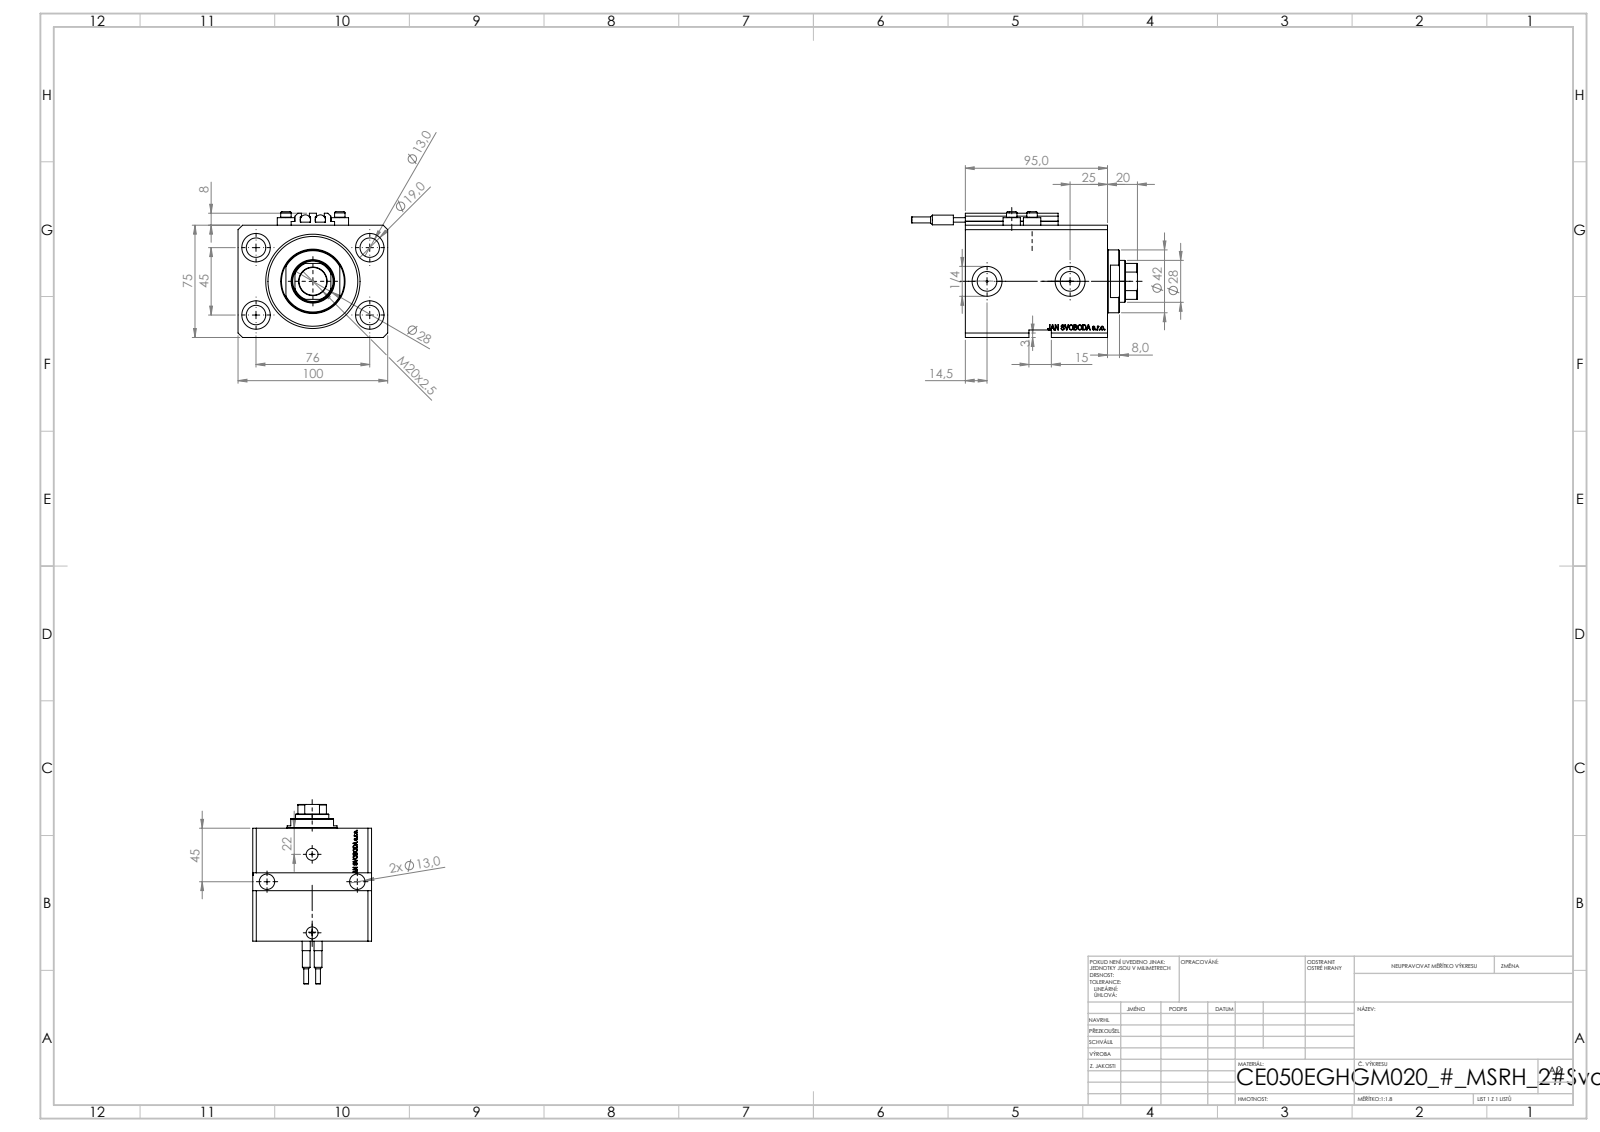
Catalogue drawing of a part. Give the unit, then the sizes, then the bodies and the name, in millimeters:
Units: millimetres
Overall size (bounding box): 151 × 100 × 84
Round holes (diameter × count): ⌀13 ×6, ⌀1.25 ×4, ⌀4 ×4, ⌀19 ×4, ⌀10 ×2, ⌀13.16 ×2, ⌀20 ×2, ⌀18.5 ×1, ⌀28 ×1, ⌀50 ×1, ⌀63 ×1
Round bosses / shafts (diameter × count): ⌀11.6 ×4, ⌀7 ×4, ⌀6.8 ×2, ⌀6.5 ×2, ⌀4 ×2, ⌀42 ×1
Partial cylindrical surfaces — rounded edges, fillets, slot ends (radius × count): R0.2 ×10, R13.5 ×1
Main face-to-face distances: 75, 100, 20, 95, 11.9, 83.1, 63.1, 5, 13, 40
Hole centre spacings: 44.16, 76, 13.6, 20.72, 27.59, 29.58, 30, 33.62
Volume: 614 551 mm³ · Surface area: 124 643 mm²
Bodies: 10 solids, 1140 faces (567 planar, 138 cylindrical, 435 other)
Part name (STEP PRODUCT): V250CE_E_Body; SWITCH_V250CE; V250CE_VC_E; ALLEN BOLT V250CE (+1 more)
STEP written by: SolidWorks 2019 (CONFIG_CONTROL_DESIGN)
